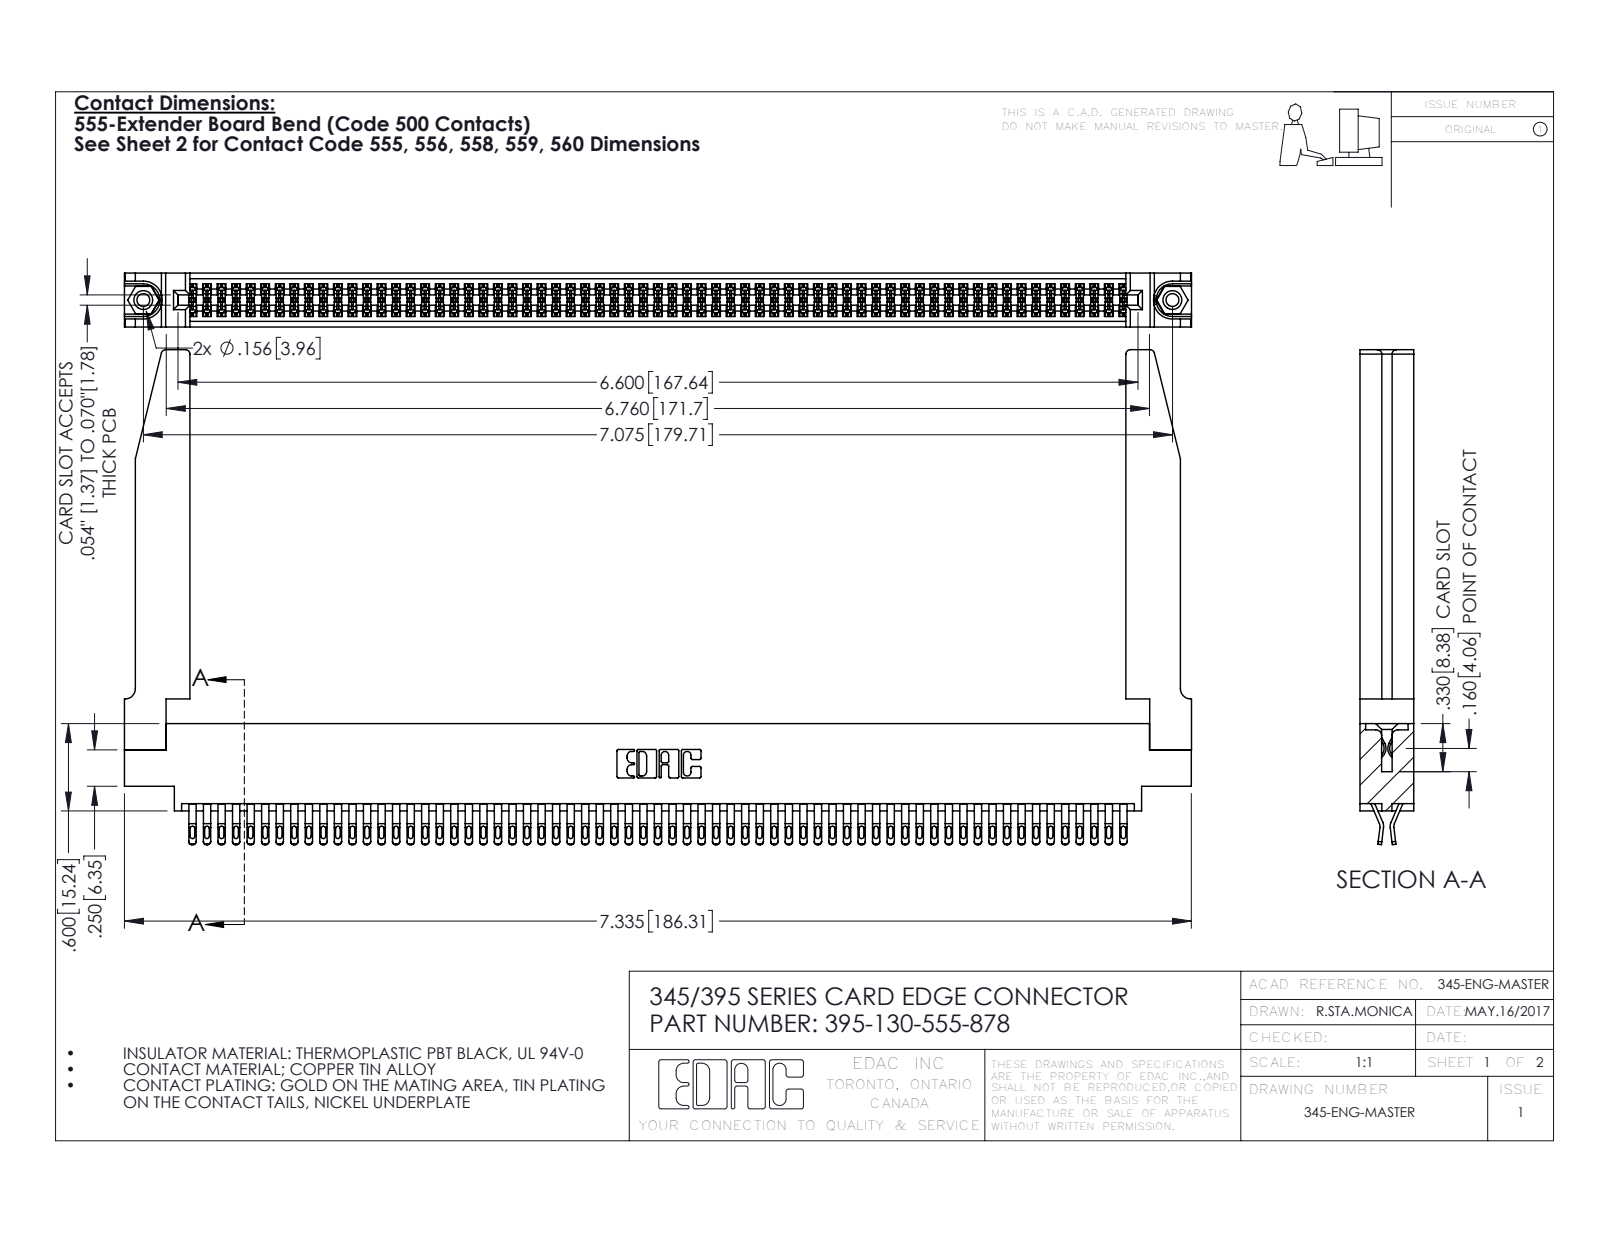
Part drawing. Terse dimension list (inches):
name: 395-130-555-878; 345-292-001_555 Tail; 345 Part_0.170 Offset - 0.156 Dia-TH; 345-250-001_345-250-001-102 (+1 more)
written by: SolidWorks 2016 (CONFIG_CONTROL_DESIGN)
unit: in
bodies: 135 solids, 7644 faces (4256 planar, 3336 cylindrical, 52 other)
size: 7.336 × 3.402 × 0.37
volume: 1.608 in³; area: 56.11 in²
holes: 2× ⌀0.089, 2× ⌀0.125, 2× ⌀0.156, 1× ⌀0.064
bosses: 2× ⌀0.155
rounds: 325× R0.016, 260× R0.02, 195× R0.006, 22× R0.01, 8× R0.03, 6× R0.007, 6× R0.031, 3× R0.026
face distances: 0.072, 0.37, 0.298, 0.025, 0.098, 0.272, 0.2, 0.225, 0.175, 0.148
hole spacings: 0.27, 6.839, 7.075
